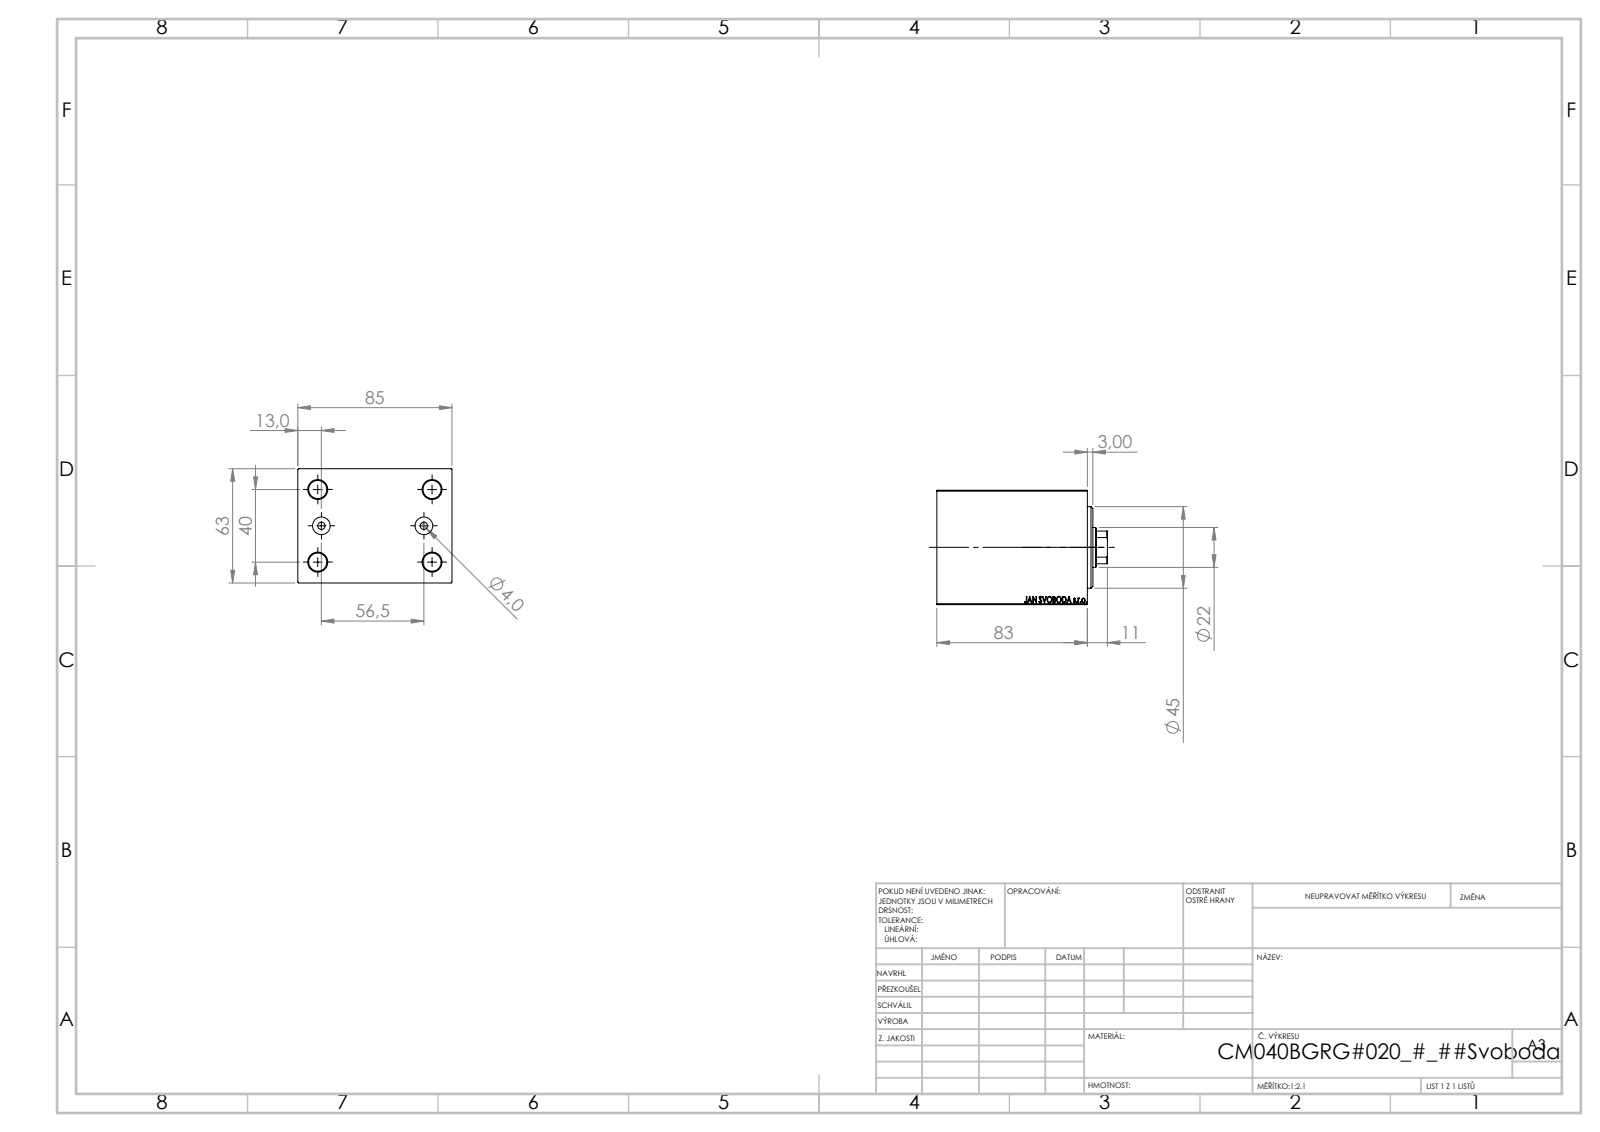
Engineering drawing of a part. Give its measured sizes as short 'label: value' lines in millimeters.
name: V450CM_B_VCP; V450CM_VC_B; V450CM_B_Body
written by: SolidWorks 2019 (CONFIG_CONTROL_DESIGN)
unit: mm
bodies: 3 solids, 877 faces (401 planar, 50 cylindrical, 426 other)
size: 94 × 85 × 63
volume: 423 707 mm³; area: 65 196 mm²
holes: 4× ⌀10, 2× ⌀4, 2× ⌀9.72, 1× ⌀12.5, 1× ⌀22, 1× ⌀25.5, 1× ⌀26.5, 1× ⌀40, 1× ⌀42, 1× ⌀45
rounds: 1× R10.5
face distances: 63, 85, 83, 51, 32, 21.6, 29.4, 61.4, 10, 51.4
hole spacings: 37.31, 20.1, 20.5, 40, 61.82, 63, 64.2, 74.63
